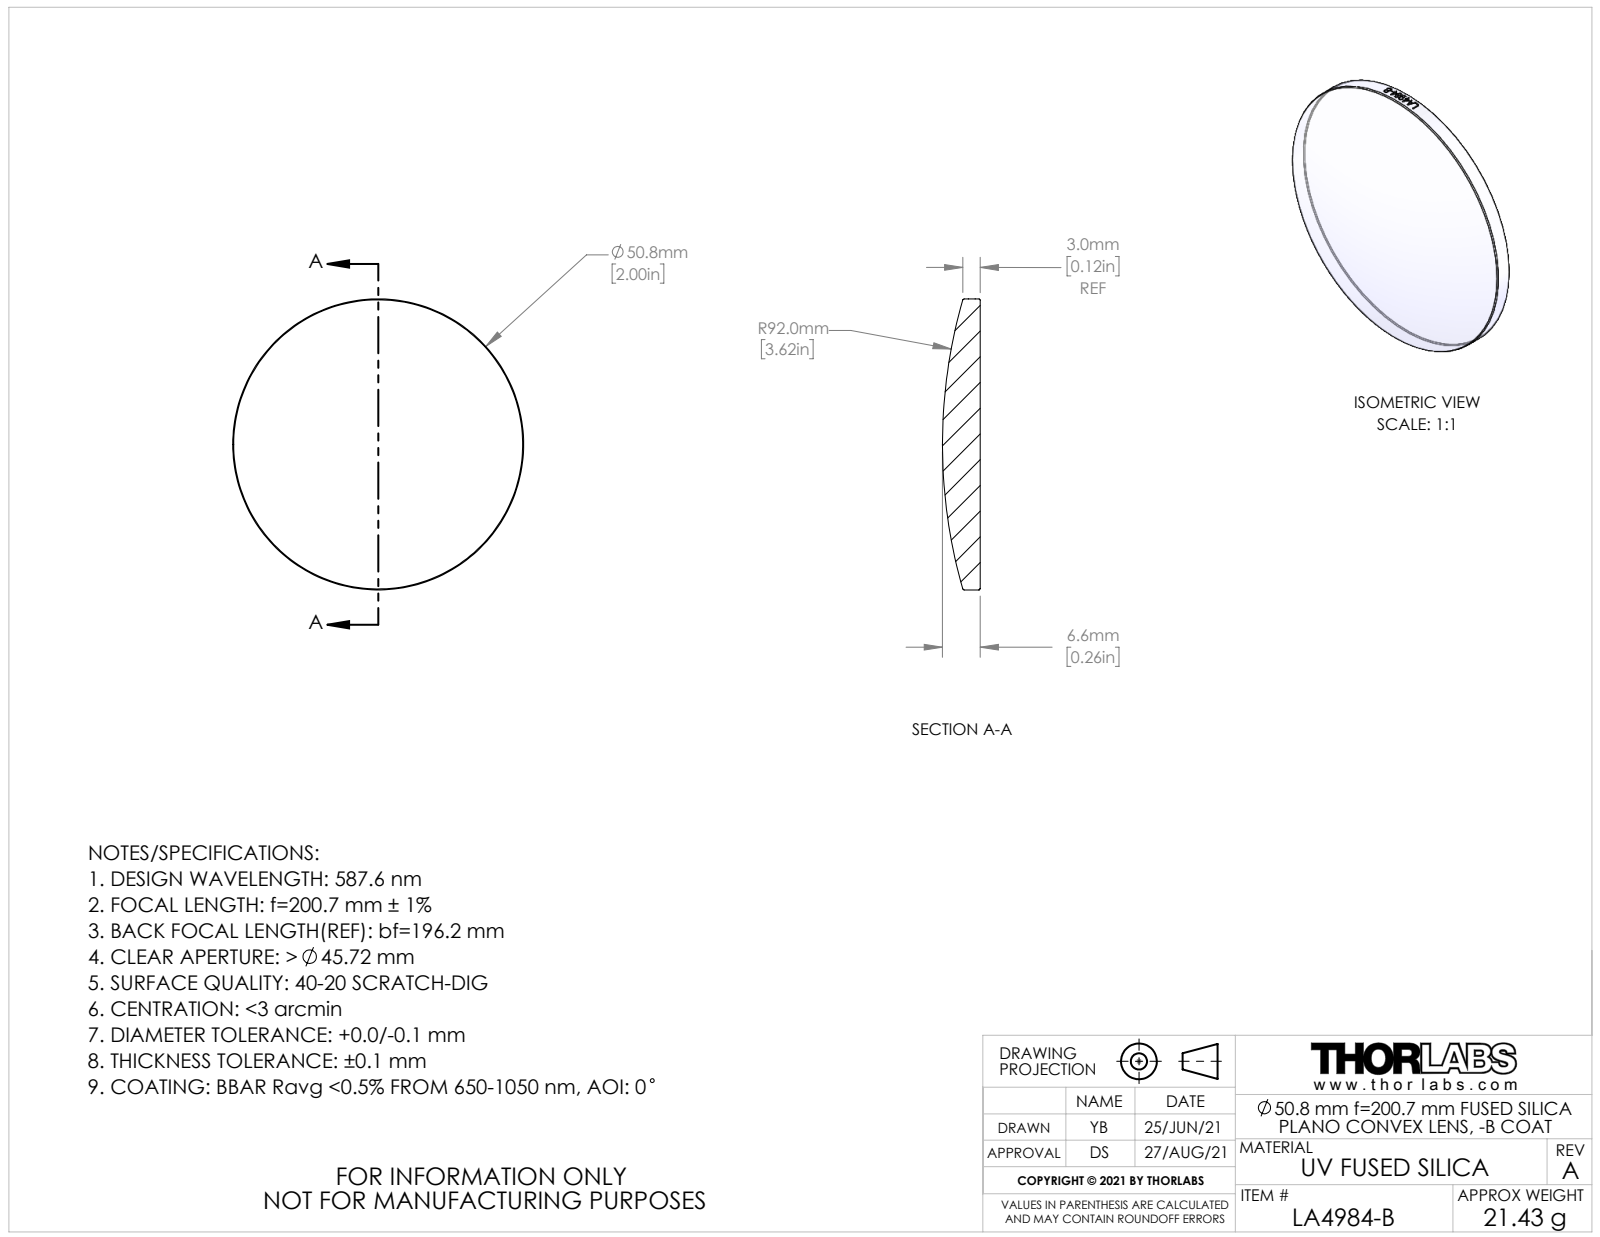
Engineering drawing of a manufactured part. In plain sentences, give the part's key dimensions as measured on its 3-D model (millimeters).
The part is named "CTN017906-E0W". Its 3-D file was written by "SolidWorks 2018 (AUTOMOTIVE_DESIGN)". It is 1 solid with 25 faces: 1 planar, 18 cylindrical and 6 other. Overall it measures 50.8 by 50.8 by 6.58 millimeters. Its volume is 9 726 cubic millimeters and its surface area 4 544 square millimeters. Round bosses or shafts: 1 of diameter 50.8.
